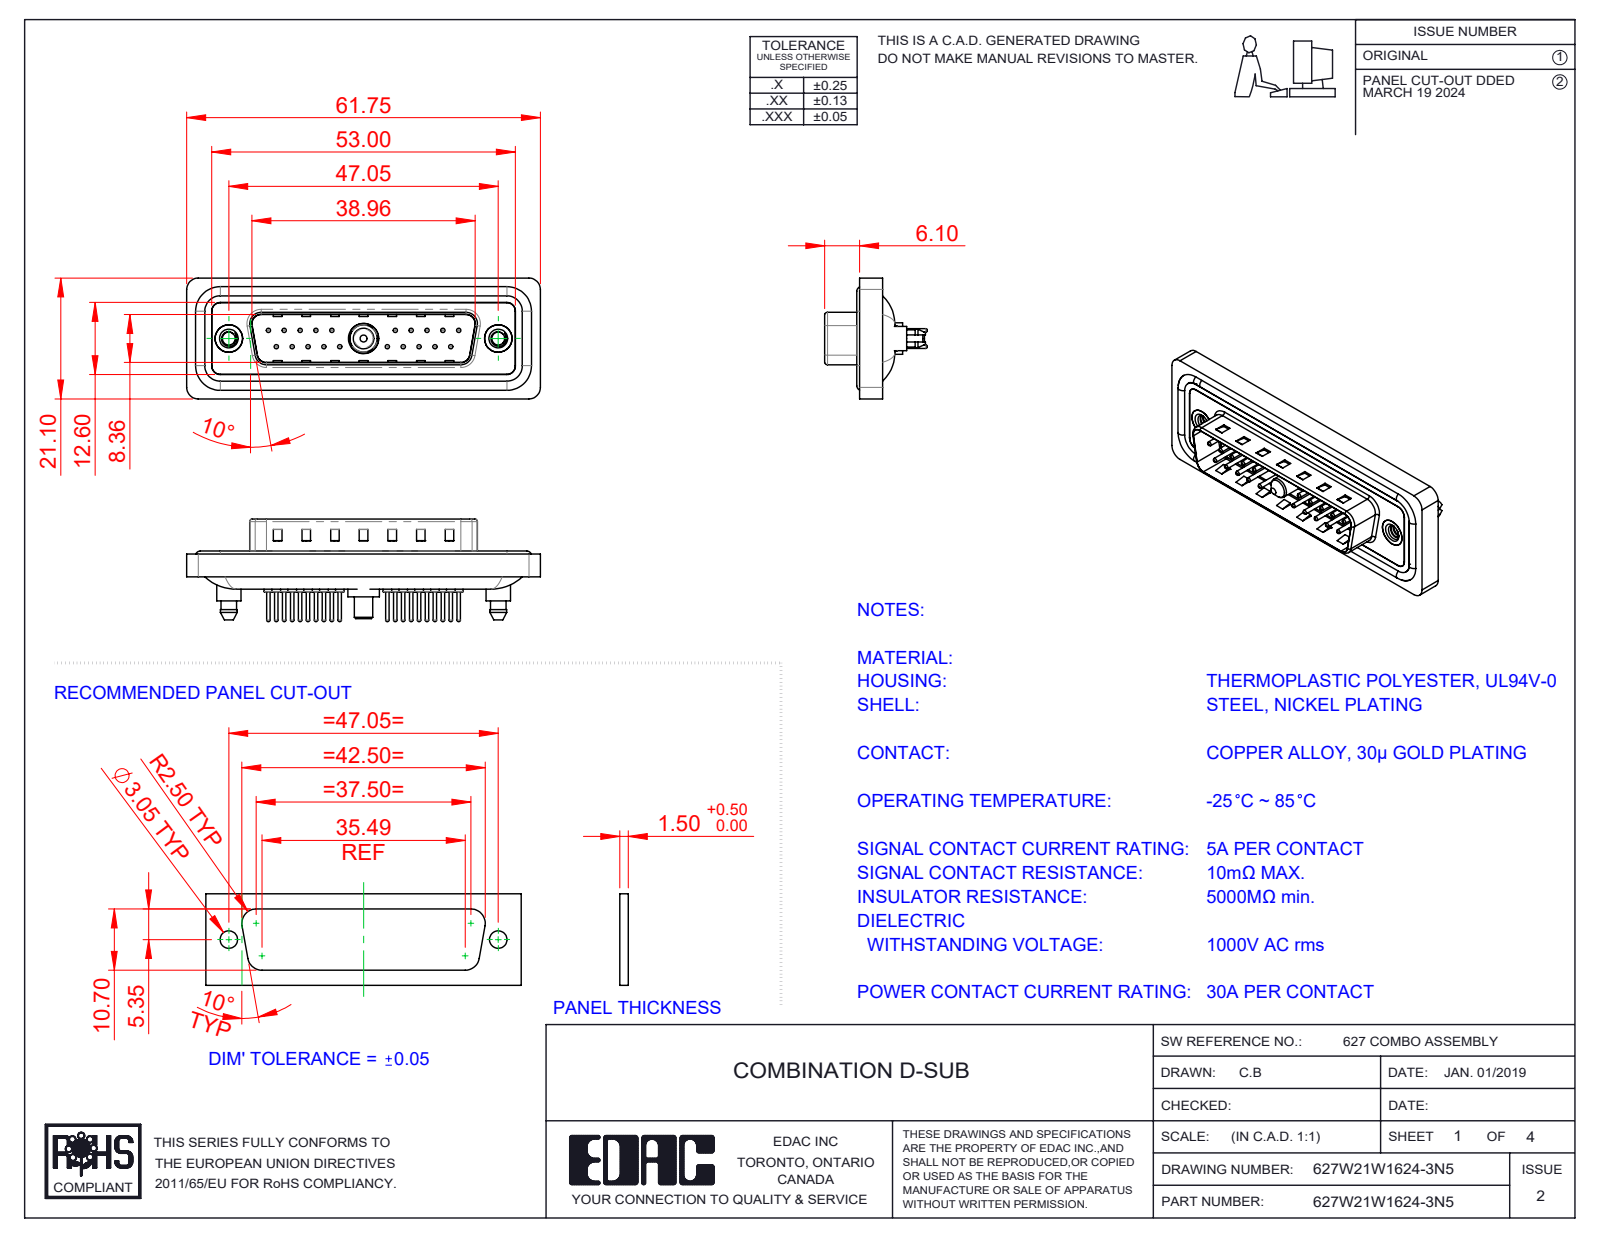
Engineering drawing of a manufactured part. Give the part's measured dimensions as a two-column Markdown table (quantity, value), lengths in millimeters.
| quantity | value |
| --- | --- |
| part name | 627Combo Shell Front_25 Contacts; 627Combo Contact Row 2_24; Power Pin_30A S; 627Combo Threaded Boardlock_5 (+5 more) |
| STEP written by | SolidWorks 2023 (CONFIG_CONTROL_DESIGN) |
| units | millimeters |
| bodies | 29 solids, 1312 faces (375 planar, 519 cylindrical, 418 other) |
| overall size | 61.75 × 21.1 × 17.9 |
| volume | 7 338 mm³ |
| surface area | 12 291 mm² |
| round holes (diameter × count) | 0.75 × 20, 1.6 × 20, 2 × 20, 2.26 × 2, 4 × 2, 4.8 × 2, 5 × 2, 4.85 × 1, 5.3 × 1 |
| round bosses / shafts (diameter × count) | 1.5 × 20, 0.6 × 20, 1.6 × 4, 5.4 × 2, 4.9 × 2, 4.25 × 2, 5.5 × 1, 5.2 × 1 |
| partial cylindrical surfaces (radius × count) | 1.5 × 24, 2 × 18, 1.6 × 10, 0.5 × 8, 0.25 × 4, 0.6 × 4, 0.65 × 4, 0.9 × 4 |
| main face-to-face distances | 0.4, 1.5, 1.1, 1.6, 0.5, 3.1, 2.9, 4.1, 0.82, 9.58 |
| hole center spacings | 3.16, 2.77, 5.54, 8.31, 5.04, 19.39, 20.97, 22.16 |
